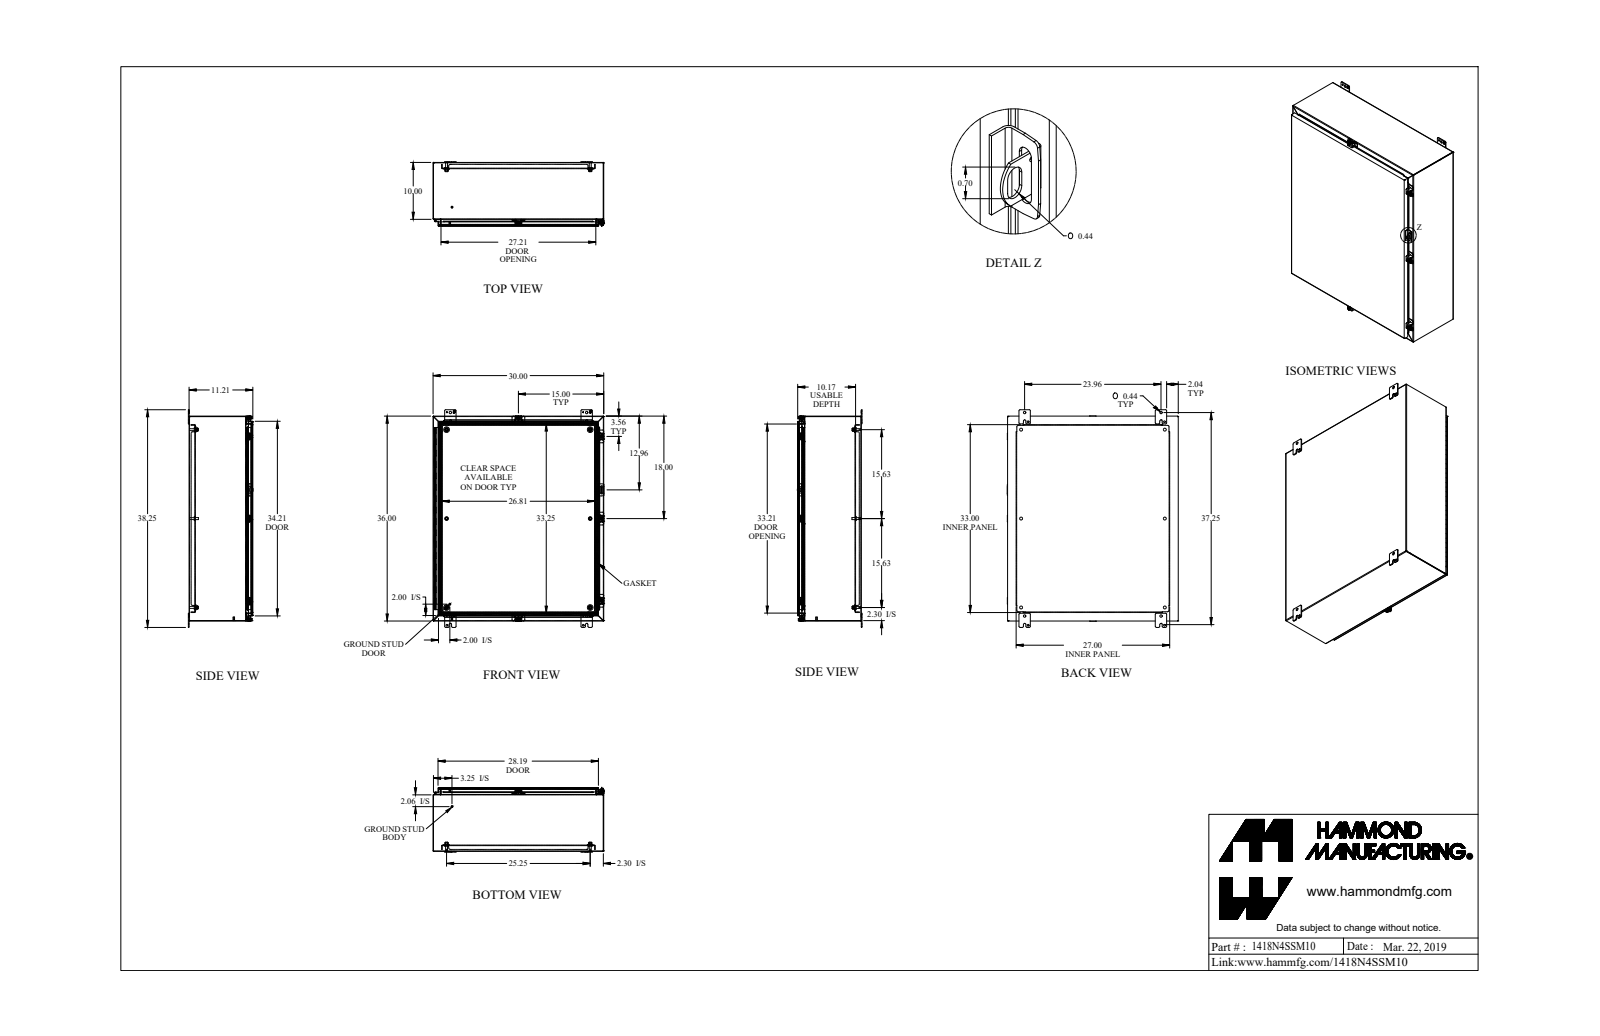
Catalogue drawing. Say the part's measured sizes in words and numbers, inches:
The part is named "1418N4SSM10_Default". Its 3-D file was written by "SolidWorks 2019 (CONFIG_CONTROL_DESIGN)". It is 49 solids with 1845 faces: 1109 planar, 630 cylindrical and 106 other. Overall it measures 38.25 by 30.063 by 11.375 inches. Its volume is 384.7 cubic inches and its surface area 10 055 square inches. Round holes: 6 of diameter 0.5, 5 of diameter 0.213, 5 of diameter 0.265, 5 of diameter 0.375, 4 of diameter 0.307, 4 of diameter 0.313, 4 of diameter 0.437, 4 of diameter 0.445, 1 of diameter 0.125, 1 of diameter 0.187. Round bosses or shafts: 6 of diameter 0.65, 6 of diameter 0.375, 6 of diameter 0.332, 5 of diameter 0.5, 5 of diameter 0.39, 5 of diameter 0.244, 4 of diameter 1, 2 of diameter 0.313. Partial cylindrical surfaces (rounded edges, fillets, slot ends): 32 of radius 0.25, 27 of radius 0.048, 27 of radius 0.143, 26 of radius 0.188, 24 of radius 0.036, 24 of radius 0.108, 12 of radius 0.125, 10 of radius 0.141. The main face-to-face distances are 0.072, 11.066, 11.138, 0.072, 11.138, 0.095, 11.21, 0.937, 1.009, 10.106. The hole center spacings are 15.625, 25.25, 12.802, 21.782, 31.25, 35.683, 43.039, 12.803.
